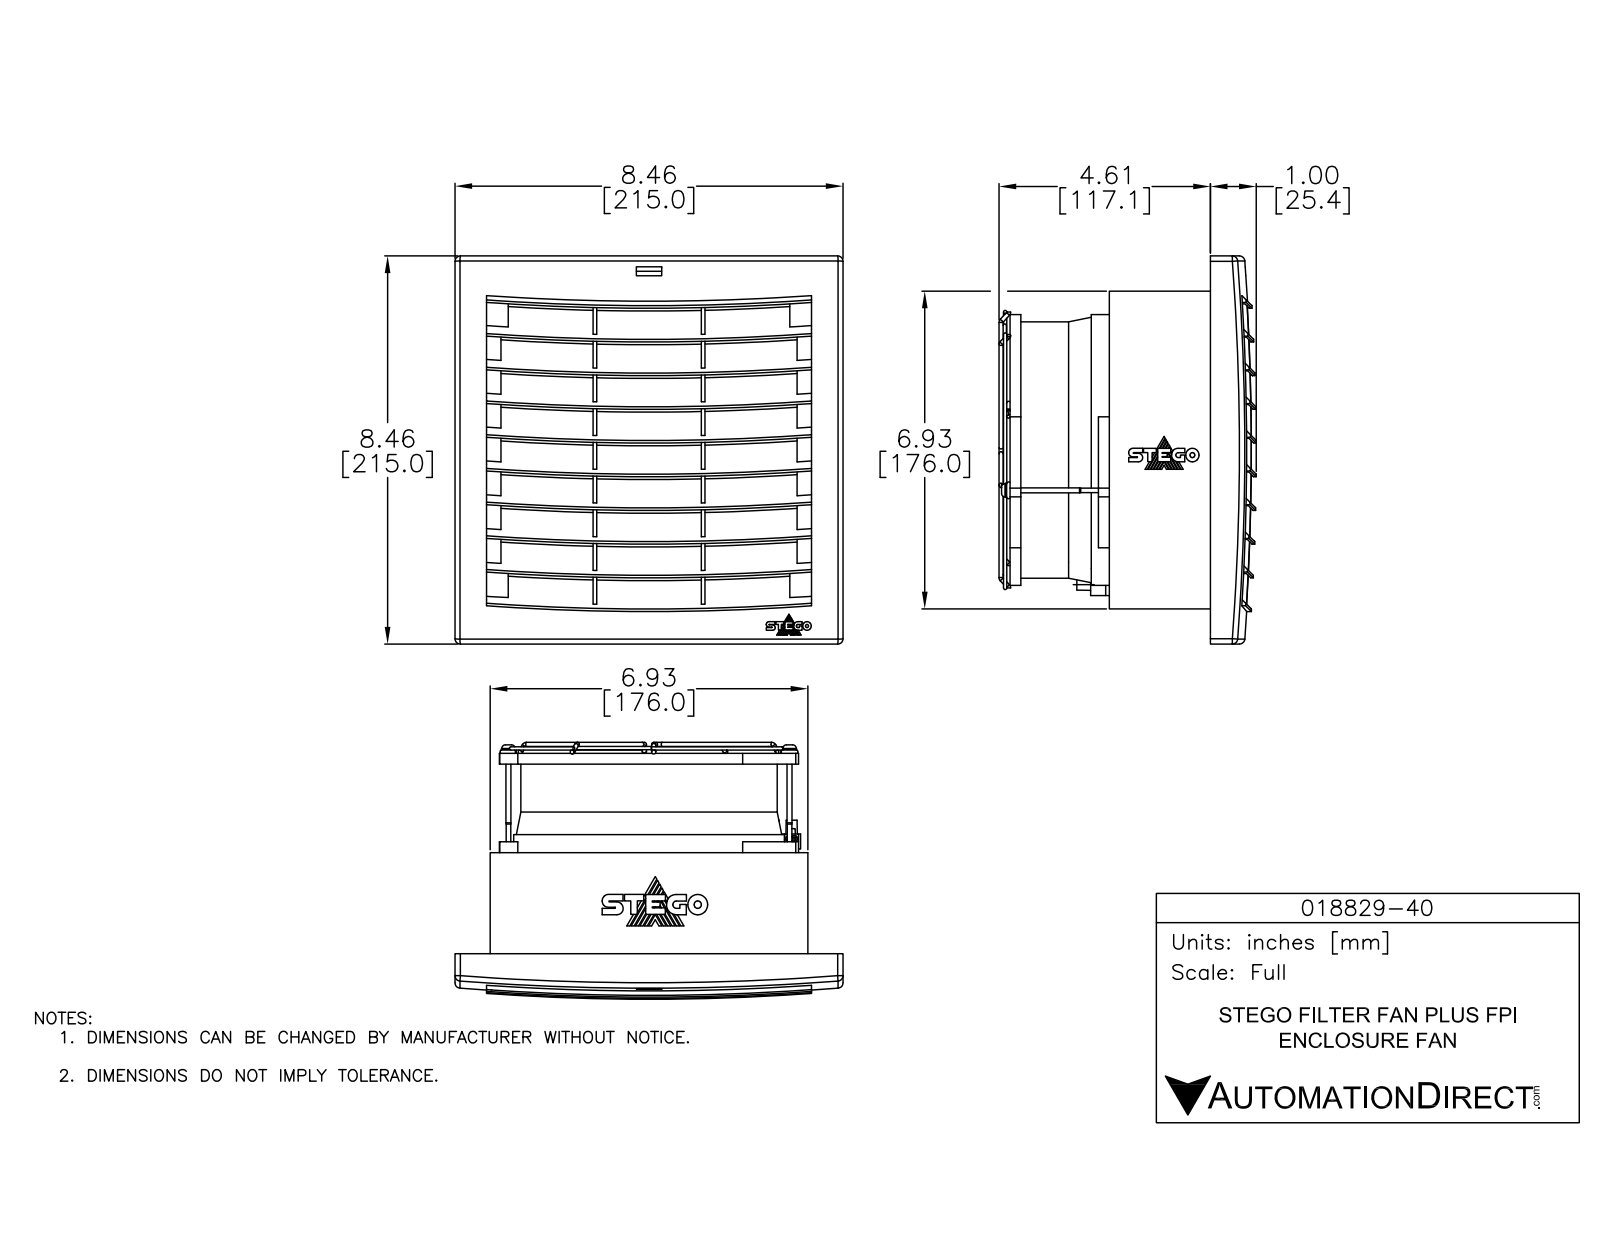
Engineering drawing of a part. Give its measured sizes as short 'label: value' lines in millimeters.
name: 018823-00
written by: SolidWorks 2017 (AUTOMOTIVE_DESIGN)
unit: mm
bodies: 1 solid, 795 faces (460 planar, 333 cylindrical, 2 other)
size: 215 × 215 × 142
volume: 1 260 000 mm³; area: 438 800 mm²
holes: 1× ⌀35.1, 1× ⌀51.4, 1× ⌀67.7, 1× ⌀79.3, 1× ⌀84, 1× ⌀100.4, 1× ⌀101.7, 1× ⌀116.7, 1× ⌀124.2, 1× ⌀136, 1× ⌀149.6
bosses: 1× ⌀161.5, 1× ⌀153, 1× ⌀130.1, 1× ⌀122.7, 1× ⌀107.7, 1× ⌀106.3, 1× ⌀90, 1× ⌀85.3
rounds: 19× R701.4, 5× R62.6, 4× R5, 4× R5.1, 2× R14, 1× R18.7, 1× R28.4, 1× R31.4
face distances: 1.5, 23.9, 4.9, 47.8, 3, 4.4, 171.6, 11.9, 11.9, 25.4
